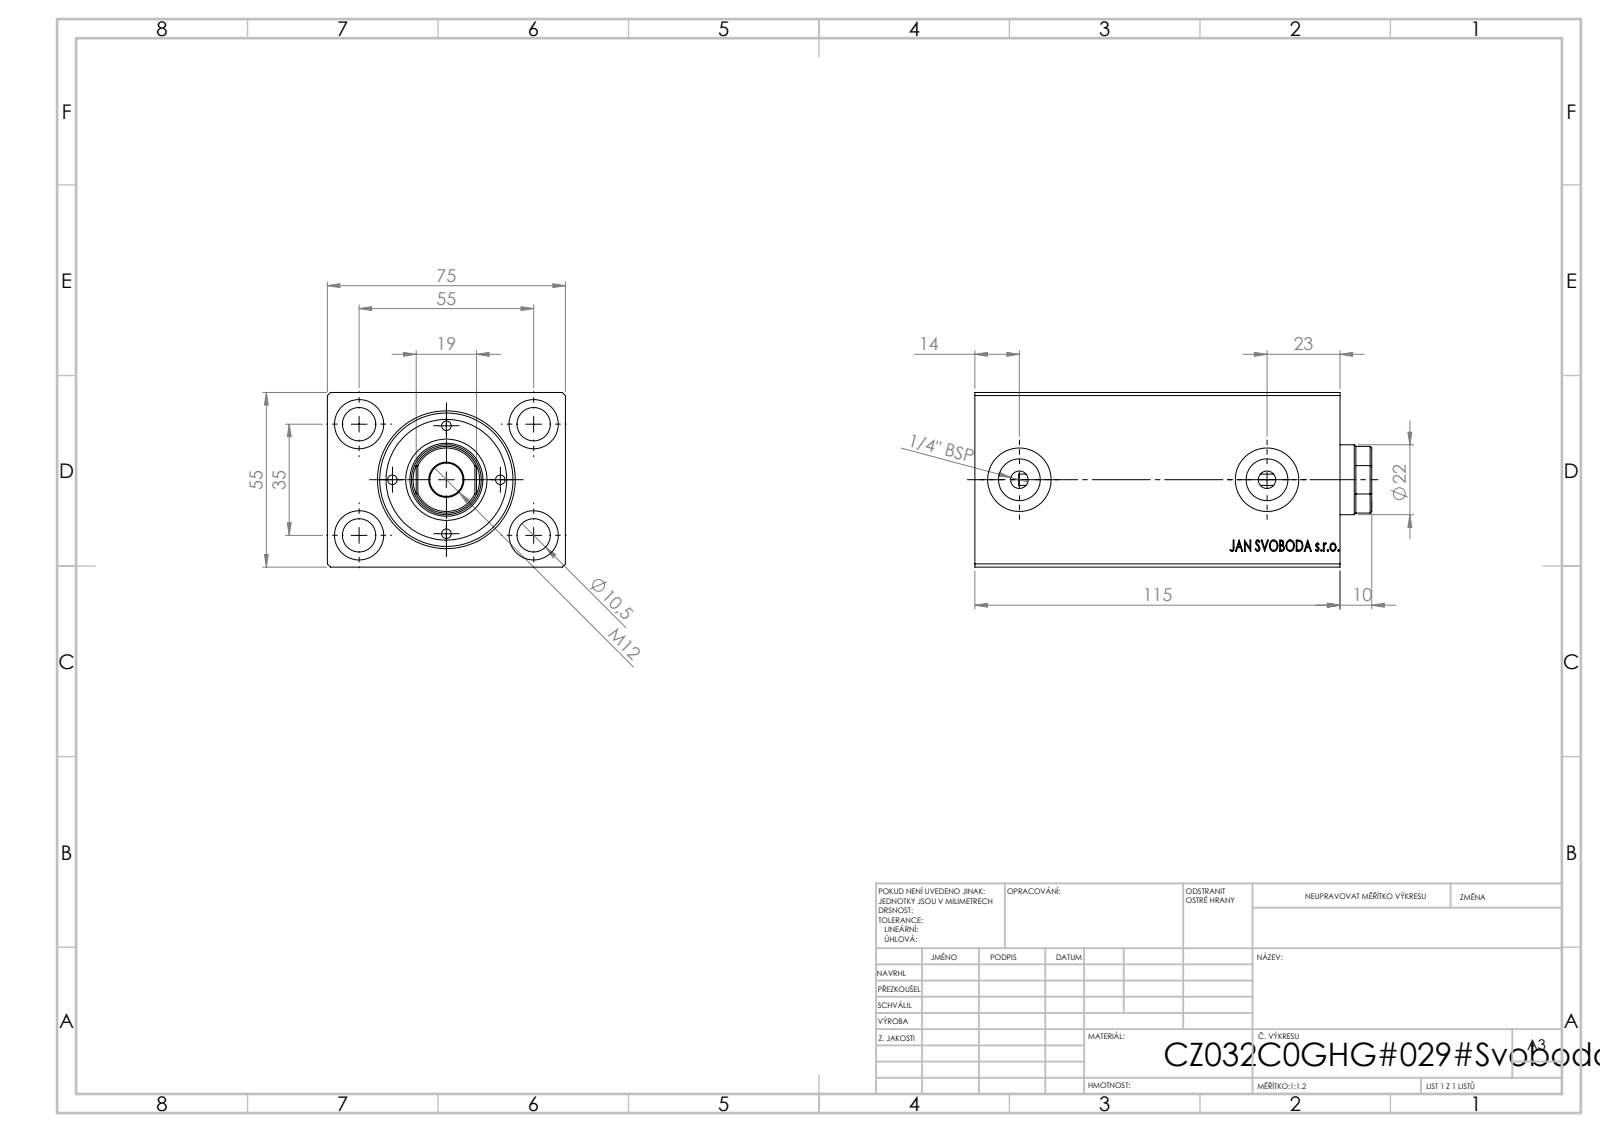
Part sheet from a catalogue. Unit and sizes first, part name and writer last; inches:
Units: inches
Overall size (bounding box): 4.528 × 2.953 × 2.165
Round holes (diameter × count): ⌀0.413 ×4, ⌀0.61 ×4, ⌀0.217 ×2, ⌀0.315 ×2, ⌀0.518 ×2, ⌀0.787 ×2, ⌀1.26 ×1, ⌀1.417 ×1, ⌀1.654 ×1
Main face-to-face distances: 2.165, 2.953, 4.528, 0.535, 4.52, 0.407, 4.121, 3.984, 0.543, 0.394
Hole centre spacings: 1.283, 1.378, 2.165, 2.567, 2.283, 3.071
Volume: 20.4 in³ · Surface area: 101.7 in²
Bodies: 1 solid, 826 faces (398 planar, 46 cylindrical, 382 other)
STEP written by: SolidWorks 2019 (CONFIG_CONTROL_DESIGN)
